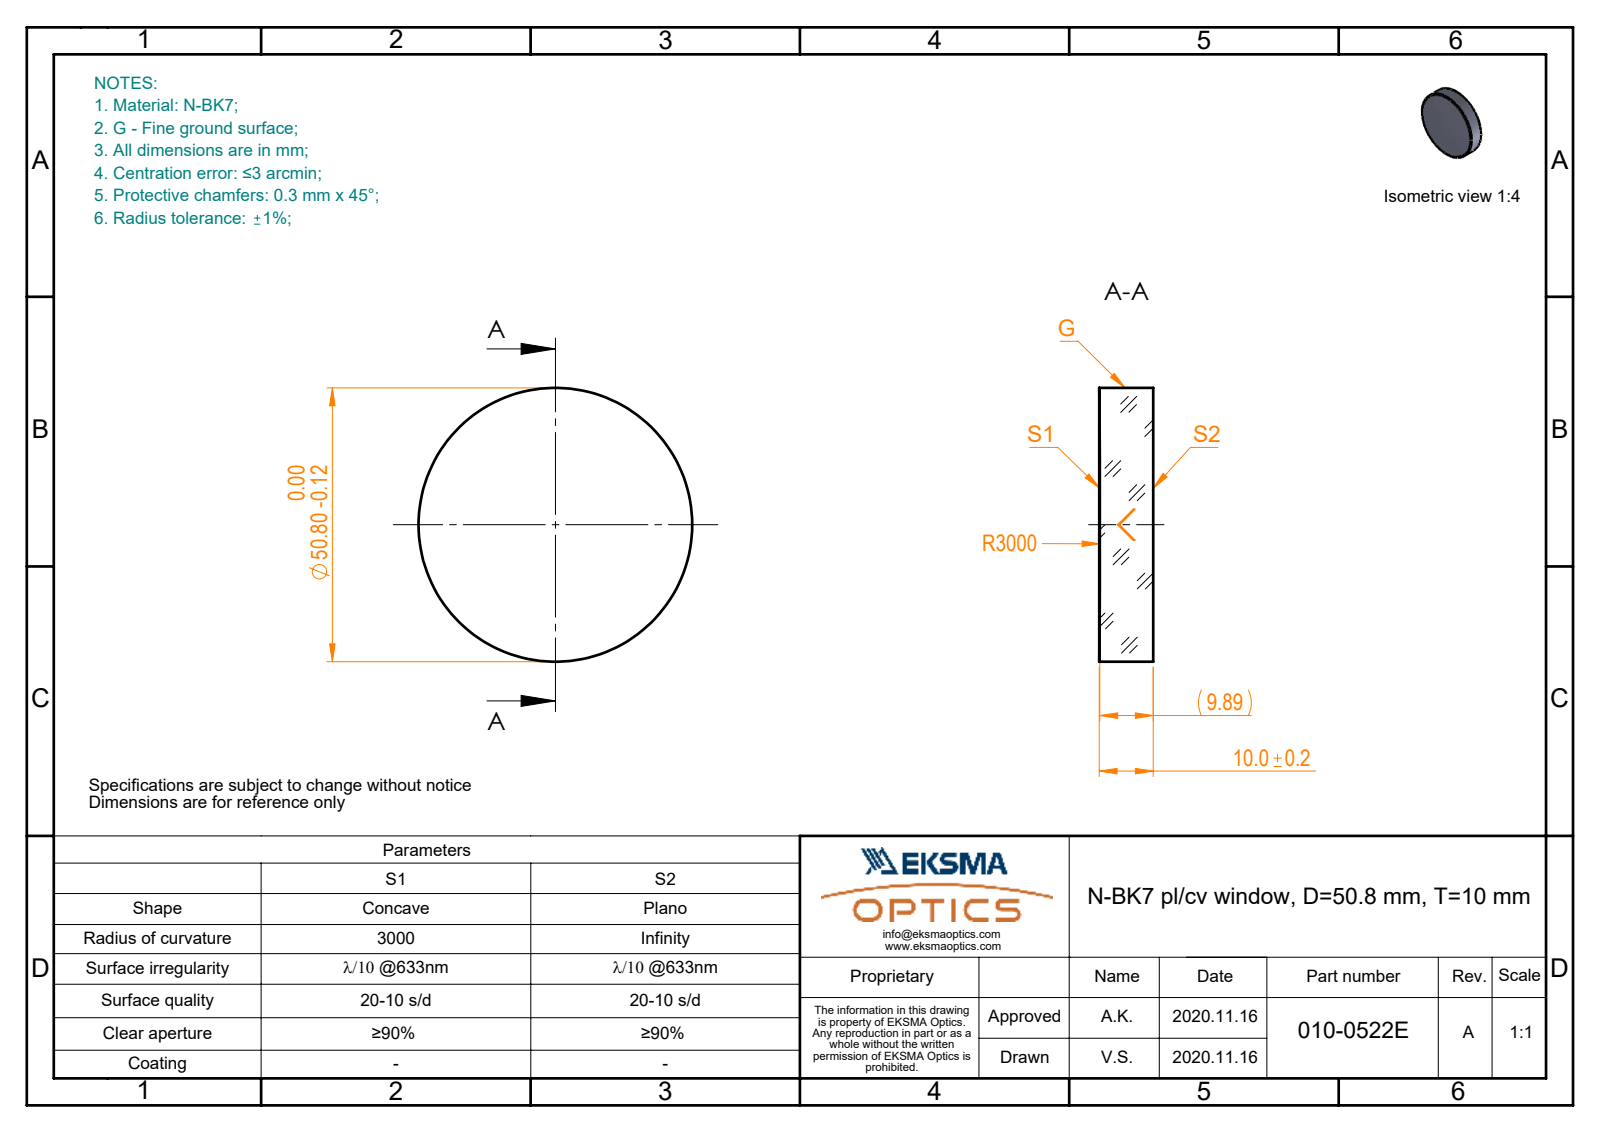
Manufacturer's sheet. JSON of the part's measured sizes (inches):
{"part_name": "010-0522E_N-BK7_PCV_window", "step_written_by": "SolidWorks 2019 (CONFIG_CONTROL_DESIGN)", "units": "inches", "bodies": {"solids": 1, "faces": 5, "planar": 1, "cylindrical": 2, "other": 2}, "overall_size": [2, 2, 0.394], "volume_in3": 1.23, "surface_area_in2": 8.758, "round_bosses_or_shafts": [[2, 1]]}
